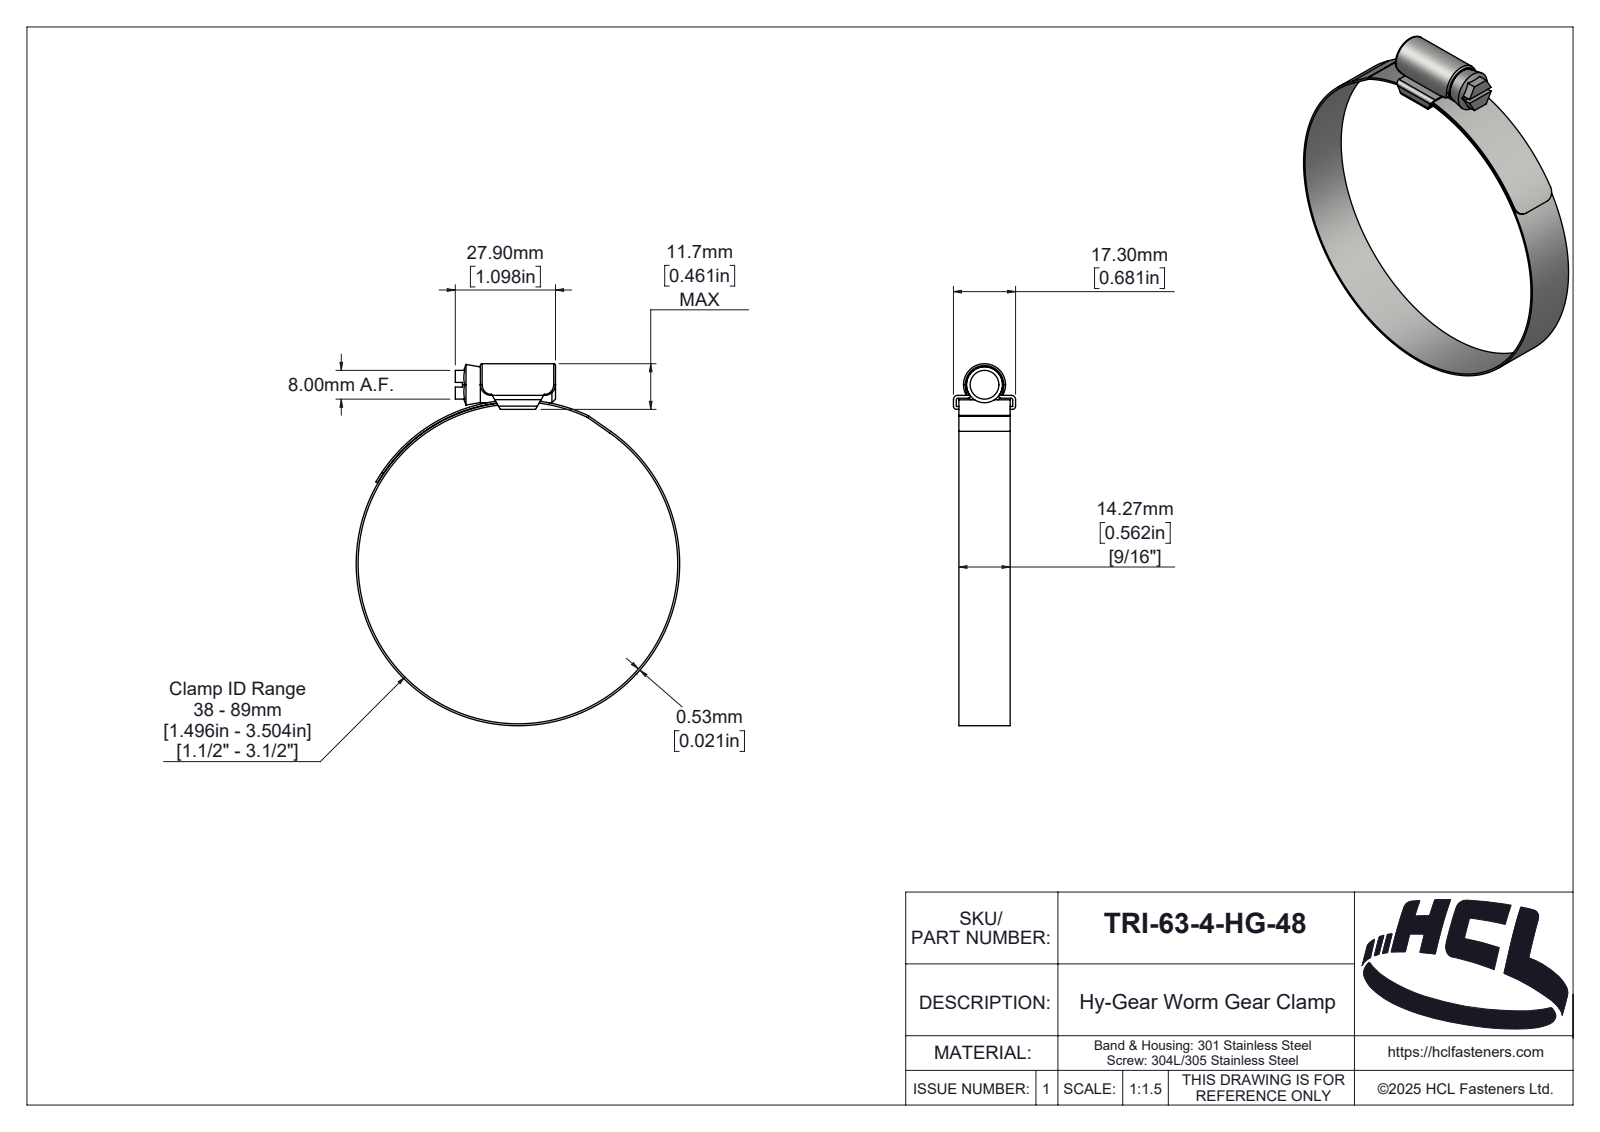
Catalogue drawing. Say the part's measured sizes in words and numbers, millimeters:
The part is named "TRI-50-0-HG-48". Its 3-D file was written by "SolidWorks 2025 (AUTOMOTIVE_DESIGN)". It is 3 solids with 189 faces: 39 planar, 89 cylindrical and 61 other. Overall it measures 100.73 by 90.06 by 17.3 millimeters. Its volume is 5 280 cubic millimeters and its surface area 12 542 square millimeters. Round holes: 1 of diameter 89. Round bosses or shafts: 1 of diameter 90.06, 1 of diameter 10. Partial cylindrical surfaces (rounded edges, fillets, slot ends): 6 of radius 0.5, 4 of radius 3, 2 of radius 0.1, 2 of radius 0.9, 2 of radius 1.2, 1 of radius 0.46, 1 of radius 1.89, 1 of radius 2. The main face-to-face distances are 0.8, 14.26, 3.1, 0.53, 2.3, 3.9, 27.9, 1.52, 15.78, 16.5.
